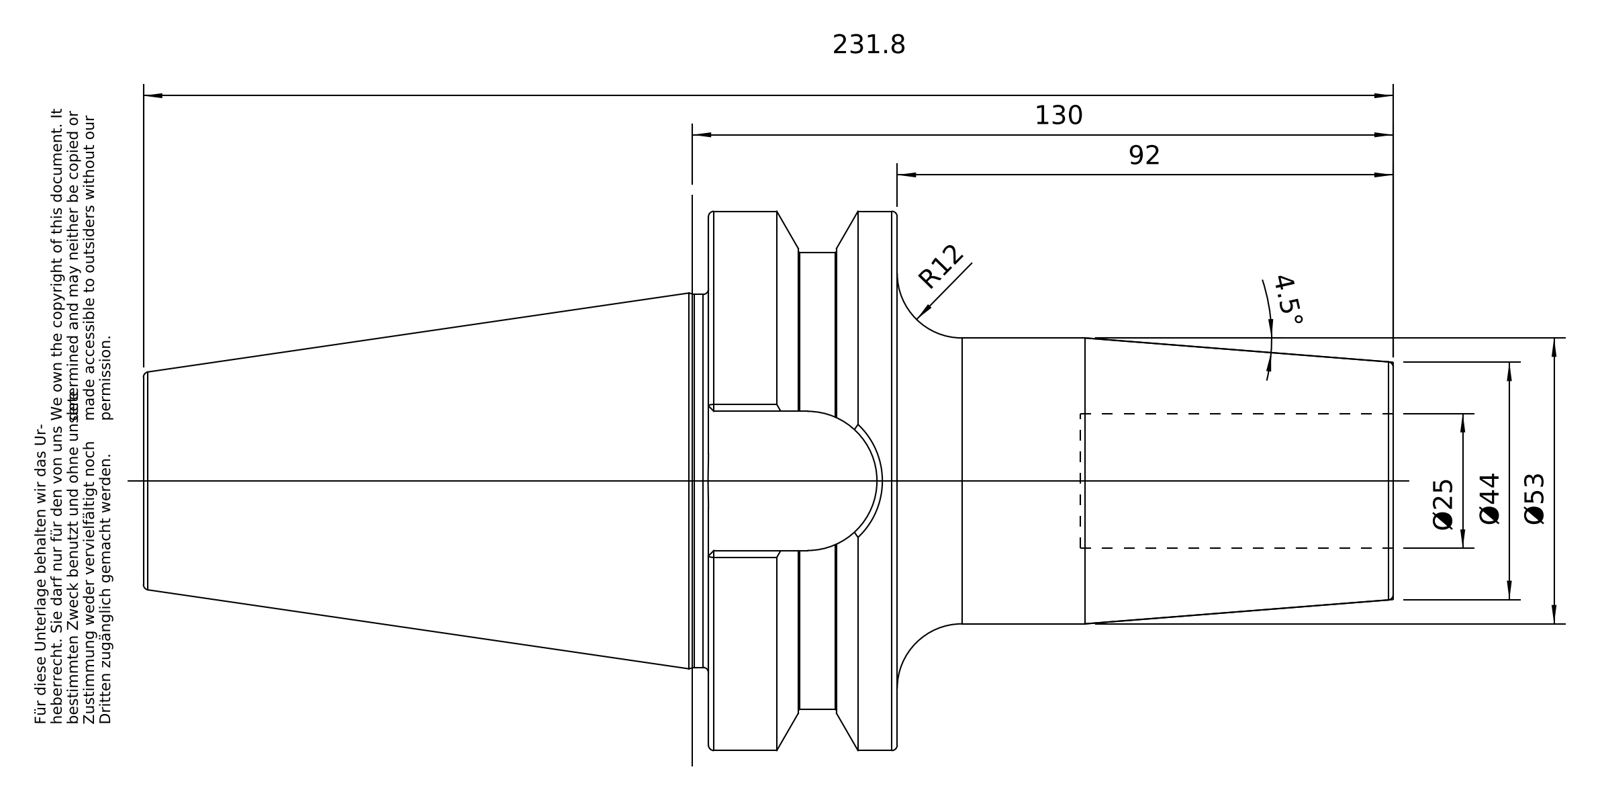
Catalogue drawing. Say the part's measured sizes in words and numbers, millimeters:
The part is named "50-644-25". Its 3-D file was written by "PRO/ENGINEER BY PARAMETRIC TECHNOLOGY CORPORATION, 2010430 (CONFIG_CONTROL_DESIGN)". It is 1 solid with 96 faces: 26 planar, 22 cylindrical and 48 other. Overall it measures 231.8 by 99.97 by 99.97 millimeters. Its volume is 627 978 cubic millimeters and its surface area 69 411 square millimeters. Round holes: 1 of diameter 20.75, 1 of diameter 25, 1 of diameter 25.02, 1 of diameter 25.7. Round bosses or shafts: 1 of diameter 99.97, 1 of diameter 84.75, 1 of diameter 69.15, 1 of diameter 53, 1 of diameter 24.01. Partial cylindrical surfaces (rounded edges, fillets, slot ends): 1 of radius 12.9. The main face-to-face distances are 35, 127, 92, 70.4, 104.8, 139.8, 231.8, 173.8, 69, 34.
